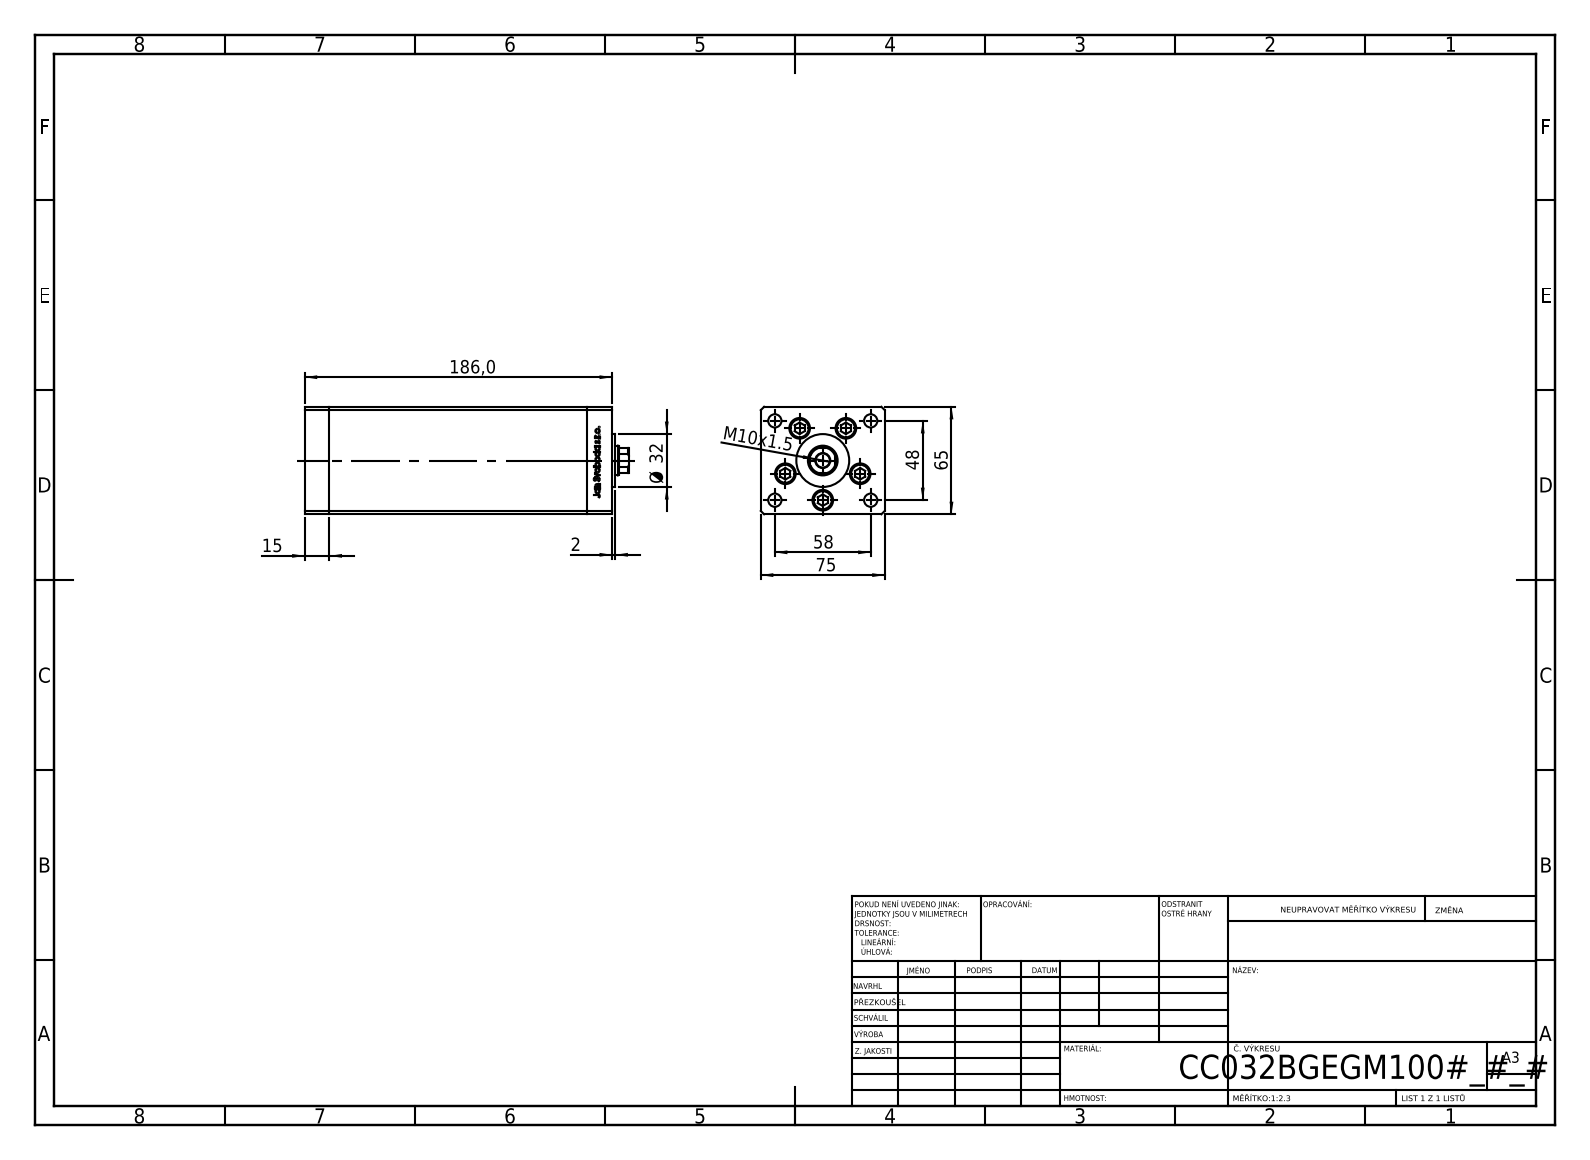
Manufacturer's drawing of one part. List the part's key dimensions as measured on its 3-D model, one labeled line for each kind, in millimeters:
Part name (STEP PRODUCT): V220C_B MIDDLE; V220C_FRONT_B; ALLEN BOLT; V220C BACK_B (+1 more)
STEP written by: SolidWorks 2019 (CONFIG_CONTROL_DESIGN)
Units: millimetres
Bodies: 14 solids, 1183 faces (462 planar, 147 cylindrical, 574 other)
Overall size (bounding box): 196 × 75 × 65
Volume: 804 978 mm³ · Surface area: 136 497 mm²
Round holes (diameter × count): ⌀9 ×5, ⌀12.5 ×5, ⌀8 ×4, ⌀2 ×2, ⌀13.16 ×2, ⌀8.5 ×1, ⌀18 ×1
Round bosses / shafts (diameter × count): ⌀8 ×5, ⌀32 ×1
Partial cylindrical surfaces — rounded edges, fillets, slot ends (radius × count): R0.93 ×2, R8.5 ×1
Main face-to-face distances: 75, 65, 15, 156, 171, 186, 28, 54.5, 10.5, 26.25
Hole centre spacings: 24, 37.64, 15.67, 17.22, 27.71, 28.83, 29, 32.63
